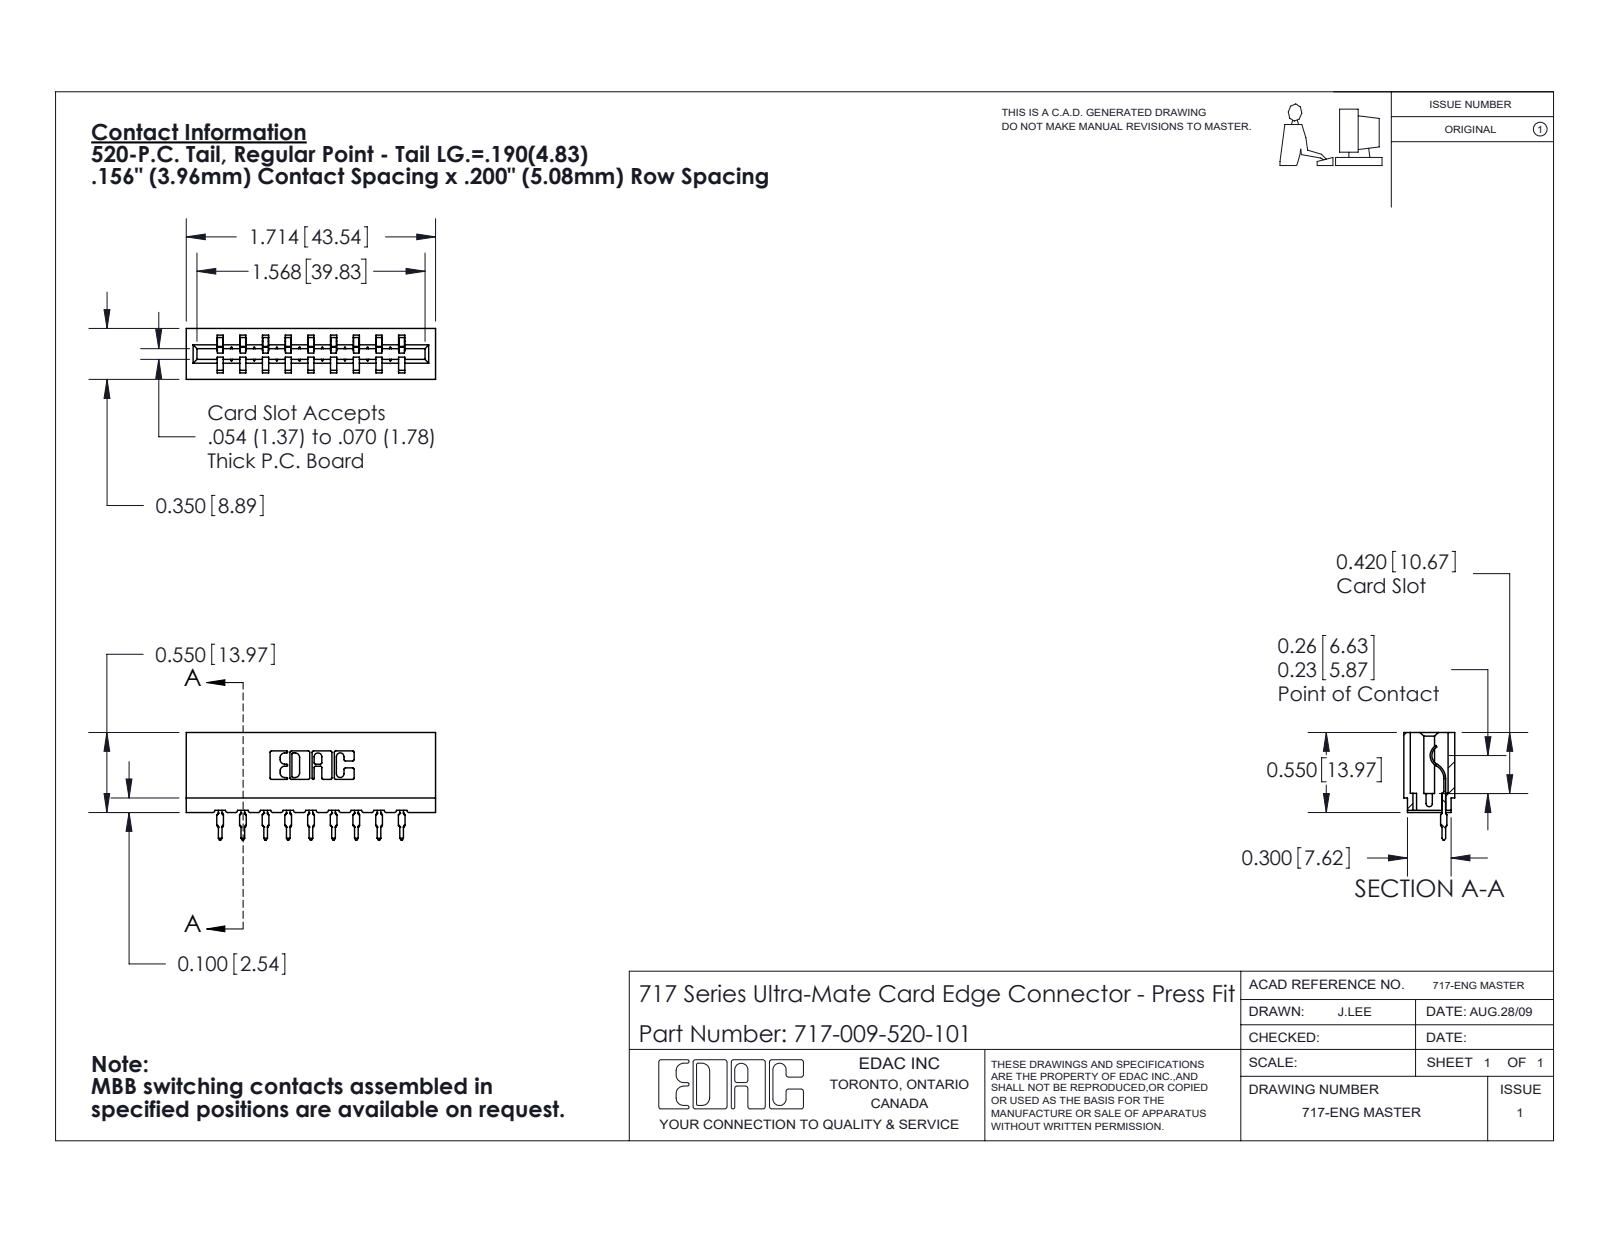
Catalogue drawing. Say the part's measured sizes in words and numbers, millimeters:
The part is named "745-292-001_520; 717 Part_Insulator Option - 06; 717-009-520-101". Its 3-D file was written by "SolidWorks 2020 (CONFIG_CONTROL_DESIGN)". It is 10 solids with 1111 faces: 666 planar, 211 cylindrical and 234 other. Overall it measures 43.5 by 18.8 by 8.9 millimeters. Its volume is 3 820 cubic millimeters and its surface area 4 934 square millimeters. Partial cylindrical surfaces (rounded edges, fillets, slot ends): 22 of radius 0.3, 18 of radius 0.4, 18 of radius 0.5, 6 of radius 0.2, 6 of radius 0.8, 4 of radius 0.1, 4 of radius 0.3, 3 of radius 0.7. The main face-to-face distances are 4, 5.4, 15.8, 3.5, 11.9, 5, 8.9, 7.9, 1.1, 7.9.
